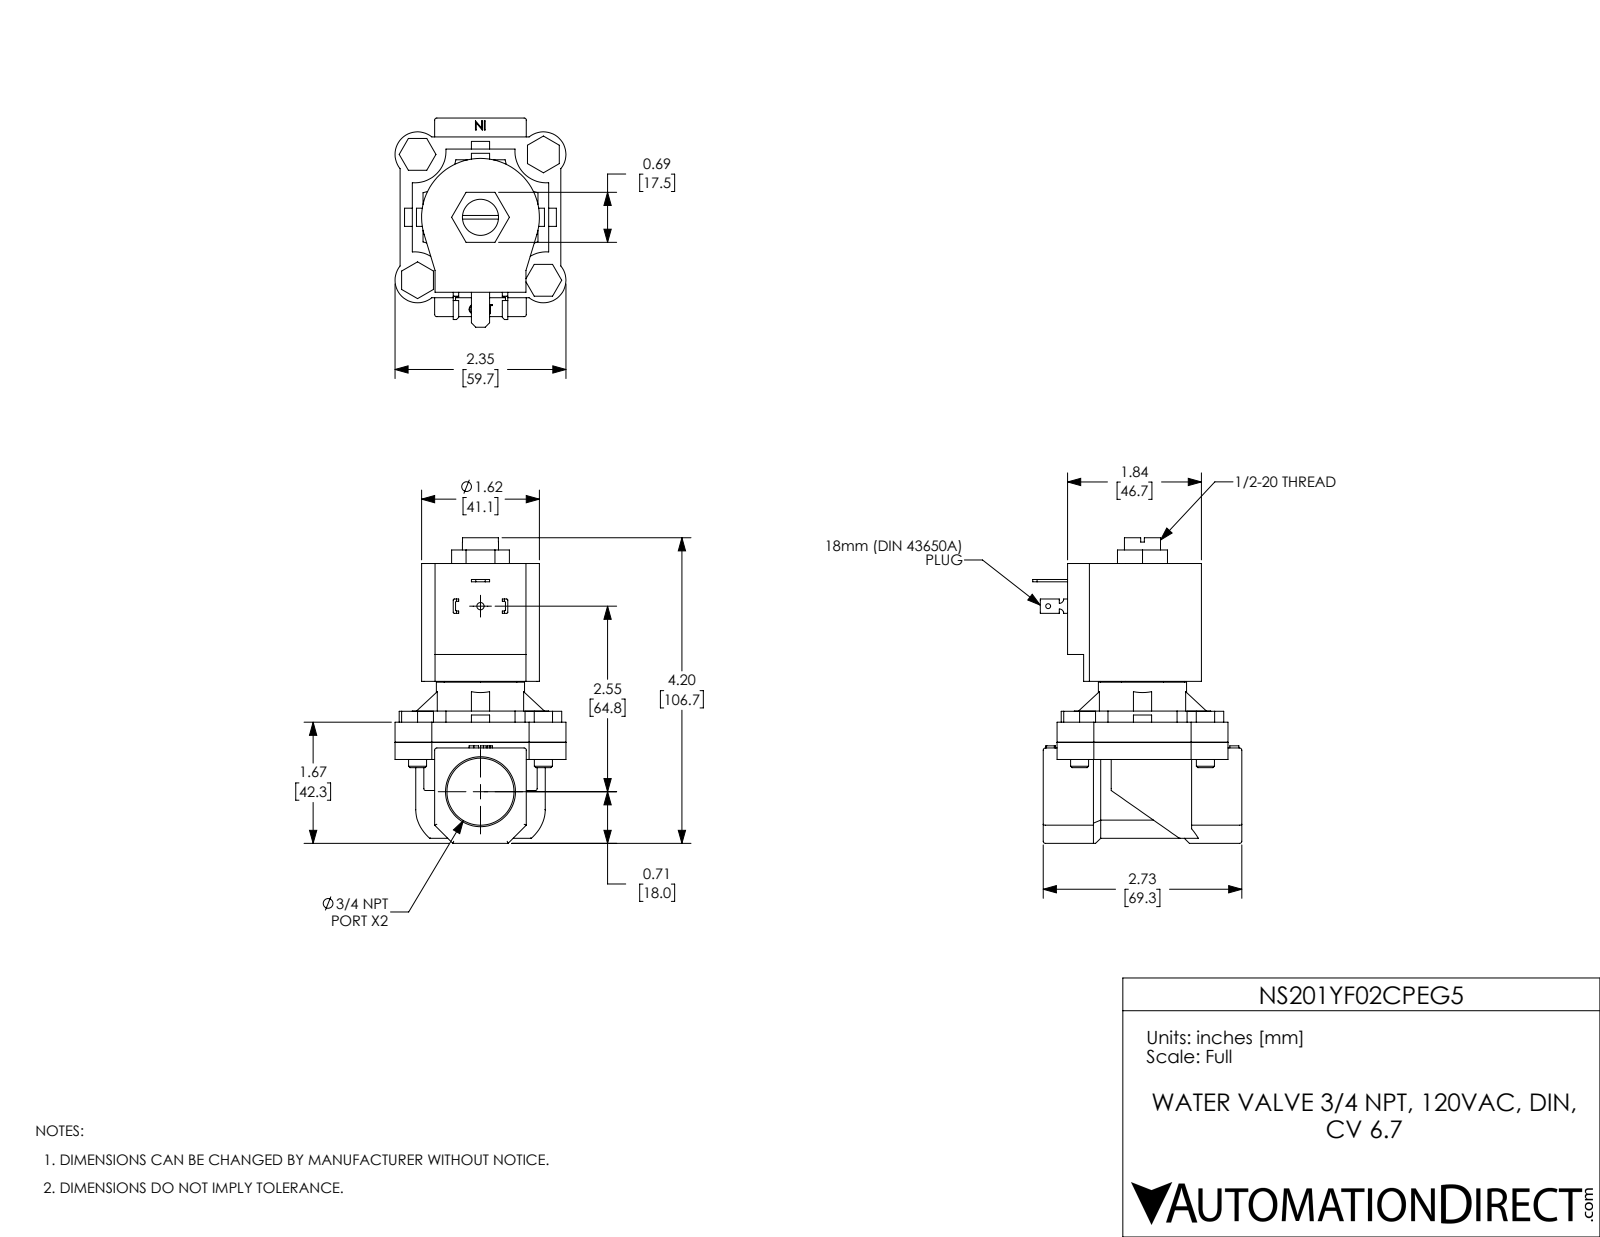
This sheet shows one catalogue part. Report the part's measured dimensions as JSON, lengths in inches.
{"part_name": "NS201YF02CPEG5", "step_written_by": "SolidWorks 2021 (CONFIG_CONTROL_DESIGN)", "units": "inches", "bodies": {"solids": 11, "faces": 387, "planar": 241, "cylindrical": 113, "other": 33}, "overall_size": [4.2, 2.875, 2.35], "volume_in3": 10.6, "surface_area_in2": 70.72, "round_holes": [[0.25, 4], [0.067, 1], [0.1, 1], [0.496, 1], [0.512, 1], [0.922, 1], [1.155, 1]], "round_bosses_or_shafts": [[0.248, 4], [1.213, 1]], "partial_cylinders_radius": [[0.03, 15], [0.015, 8], [0.31, 4], [0.432, 4], [0.579, 4], [0.06, 2], [0.81, 1], [0.89, 1]], "face_to_face_distances": [0.276, 2.457, 2.181, 0.236, 0.512, 2.693, 0.475, 1.735, 1.26, 2.21], "hole_center_spacings": [1.223, 1.73, 2.446, 2.55]}
